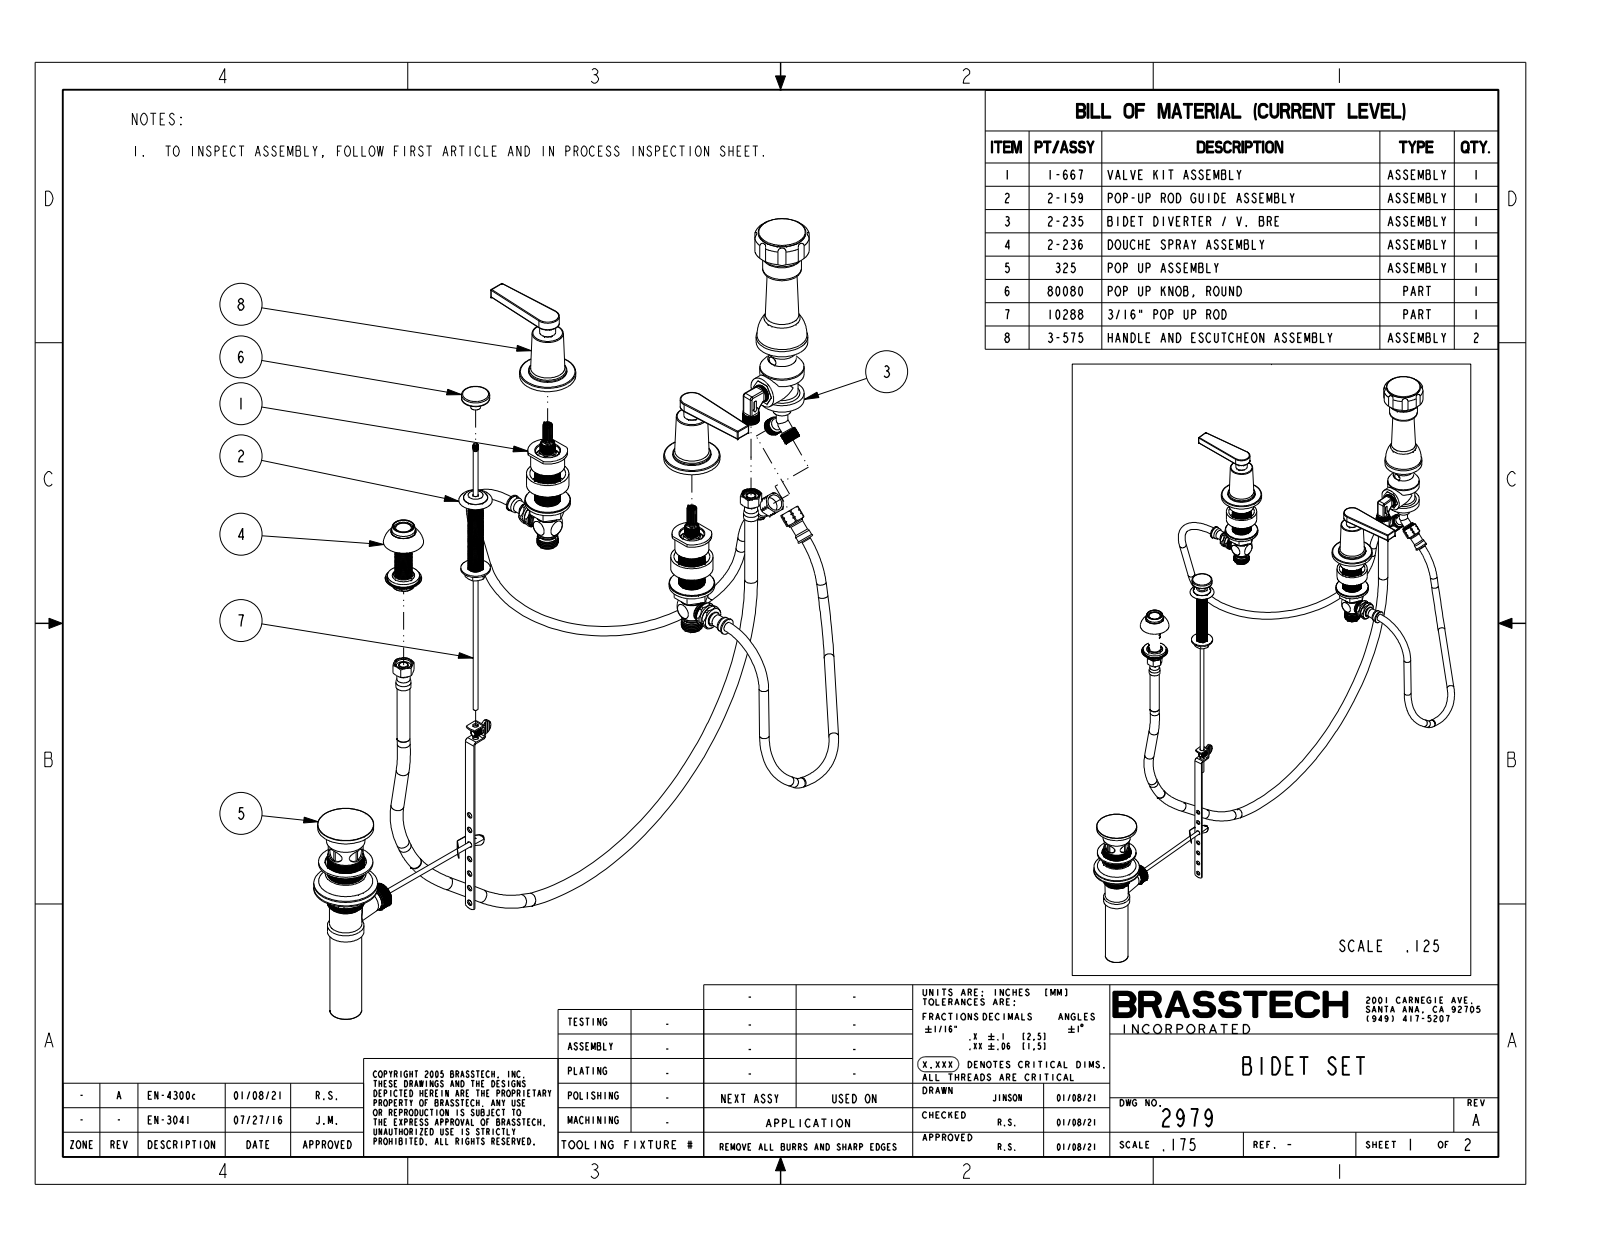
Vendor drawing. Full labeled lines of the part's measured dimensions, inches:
Part name (STEP PRODUCT): 2979
STEP written by: CREO PARAMETRIC BY PTC INC, 2018400 (CONFIG_CONTROL_DESIGN)
Units: inches
Bodies: 5 solids, 229 faces (61 planar, 84 cylindrical, 84 other)
Overall size (bounding box): 22.855 × 13.7 × 5.353
Volume: 20.72 in³ · Surface area: 100.6 in²
Round holes (diameter × count): ⌀1.3 ×2, ⌀0.625 ×1, ⌀0.792 ×1, ⌀0.94 ×1
Round bosses / shafts (diameter × count): ⌀2.2 ×2, ⌀1.5 ×2, ⌀1.275 ×2, ⌀0.625 ×2, ⌀0.525 ×2, ⌀2.025 ×1, ⌀1.52 ×1, ⌀1.1 ×1
Partial cylindrical surfaces — rounded edges, fillets, slot ends (radius × count): R0.03 ×16, R0.21 ×8, R0.46 ×2, R0.357 ×1, R1.077 ×1
Main face-to-face distances: 0.187, 2.87, 2.683, 0.375, 2.495, 2.308, 2.047, 1.86, 0.448, 0.823
Hole centre spacings: 12.649, 8
